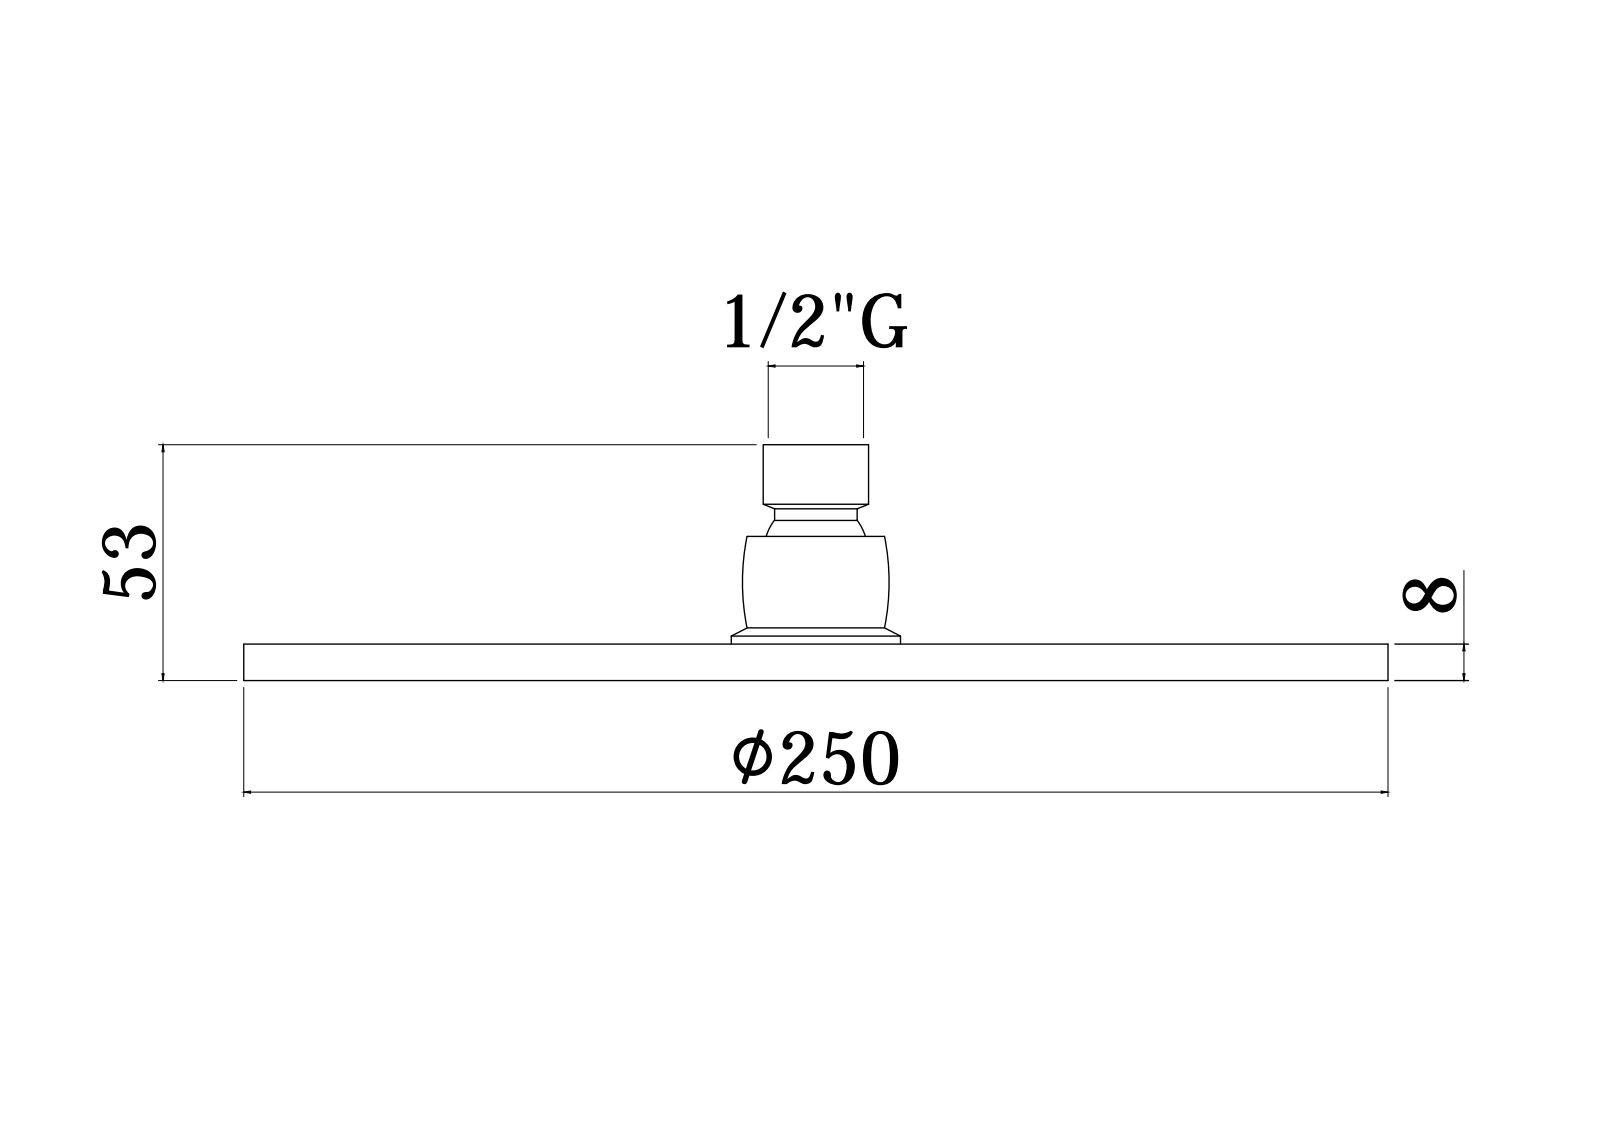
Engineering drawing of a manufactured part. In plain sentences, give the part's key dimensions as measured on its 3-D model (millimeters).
The part is named "ZSOF101CR". Its 3-D file was written by "CREO PARAMETRIC BY PTC INC, 2020044 (CONFIG_CONTROL_DESIGN)". It is 1 solid with 2749 faces: 352 planar, 658 cylindrical and 1739 other. Overall it measures 250.69 by 250.69 by 51.9 millimeters. Its volume is 228 906 cubic millimeters and its surface area 202 236 square millimeters. Round holes: 78 of diameter 1.5, 78 of diameter 1.7, 13 of diameter 7, 12 of diameter 2.5, 12 of diameter 5.1, 1 of diameter 15, 1 of diameter 16, 1 of diameter 16.5, 1 of diameter 18.63, 1 of diameter 23.1, 1 of diameter 23.8, 1 of diameter 24. Round bosses or shafts: 78 of diameter 10, 12 of diameter 6, 12 of diameter 5, 1 of diameter 250.69, 1 of diameter 245.6, 1 of diameter 31.8, 1 of diameter 28, 1 of diameter 23.2. Partial cylindrical surfaces (rounded edges, fillets, slot ends): 12 of radius 20. The main face-to-face distances are 8.5, 7.5, 1, 1.5, 6, 7, 5.6, 2.9, 1.4, 4.6. The hole center spacings are 100, 198.29, 121.75, 51.76, 141.42, 158.67, 184.78, 26.1.
